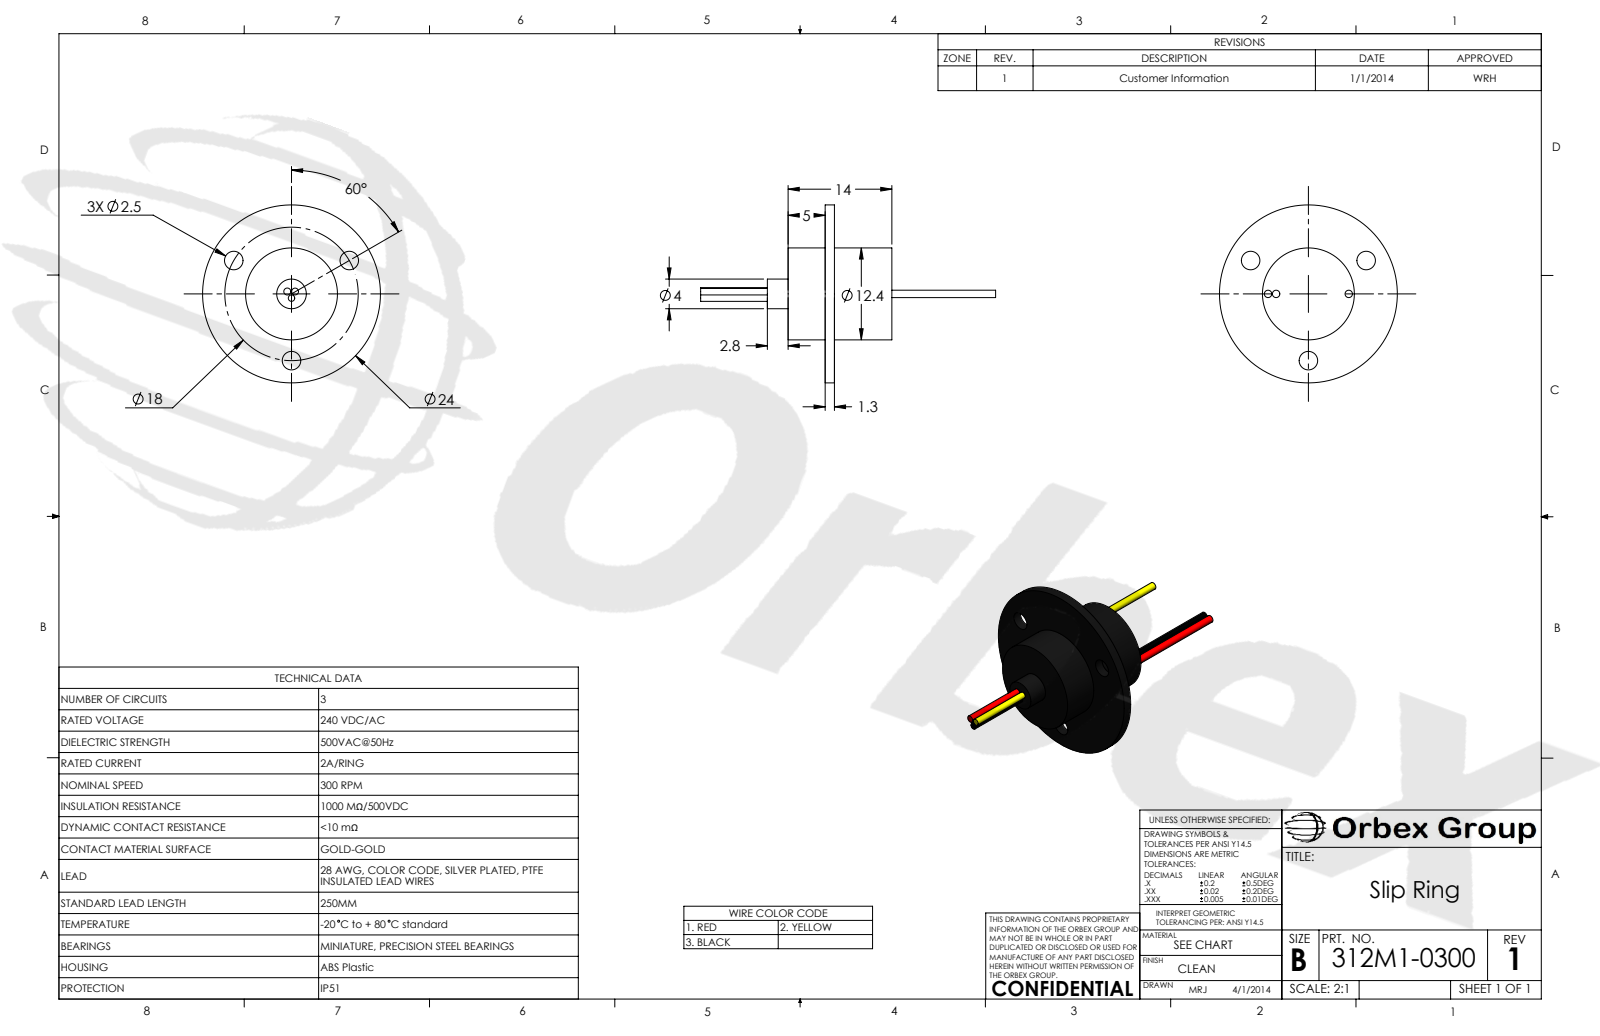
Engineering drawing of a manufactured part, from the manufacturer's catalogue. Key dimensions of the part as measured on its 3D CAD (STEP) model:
Part name (STEP PRODUCT): 312M1-0300 Rev 1
STEP written by: SolidWorks 2013 (CONFIG_CONTROL_DESIGN)
Units: millimetres
Bodies: 1 solid, 37 faces (11 planar, 26 cylindrical, 0 other)
Overall size (bounding box): 39.8 × 24 × 24
Volume: 2 173 mm³ · Surface area: 1 740 mm²
Round holes (diameter × count): ⌀2.5 ×3
Round bosses / shafts (diameter × count): ⌀1 ×3, ⌀24 ×1, ⌀12.4 ×1, ⌀4 ×1, ⌀0.94 ×1, ⌀0.92 ×1, ⌀0.87 ×1
Main face-to-face distances: 1.25, 9, 7.75, 14, 6.25, 5, 16.8, 9.05, 7.8, 2.8
Hole centre spacings: 15.59, 15.58
